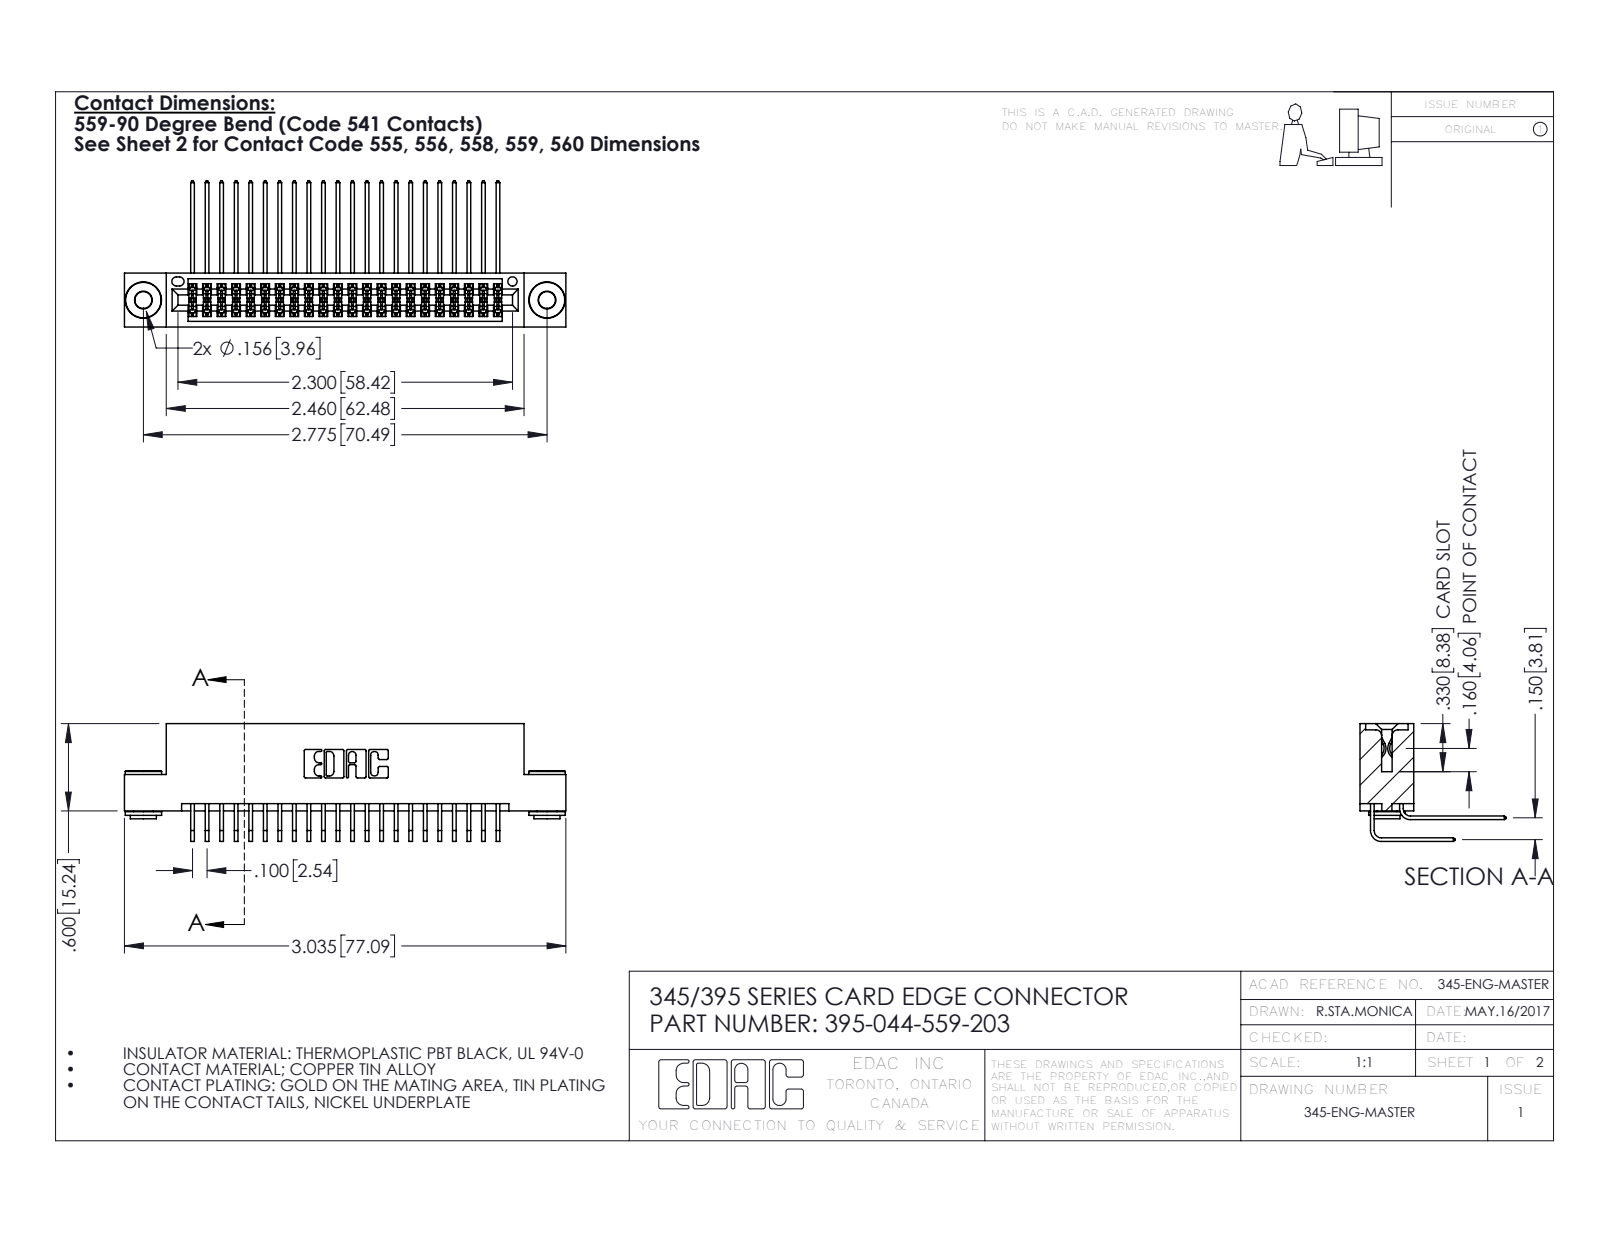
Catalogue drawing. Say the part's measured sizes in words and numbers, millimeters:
The part is named "345-292-001_558 559 Tail - 1; 345-250-002_345-250-002-102; 345 Part_Flush Mounting Lugs - 0.156 Dia-TH; 345-292-001_559 Tail - 2 (+1 more)". Its 3-D file was written by "SolidWorks 2016 (CONFIG_CONTROL_DESIGN)". It is 47 solids with 2452 faces: 1630 planar, 814 cylindrical and 8 other. Overall it measures 77.1 by 25.5 by 20.5 millimeters. Its volume is 7 570 cubic millimeters and its surface area 12 210 square millimeters. Round holes: 2 of diameter 2.9, 2 of diameter 4, 1 of diameter 1.6. Round bosses or shafts: 2 of diameter 6.4, 2 of diameter 4.6, 2 of diameter 3.5. Partial cylindrical surfaces (rounded edges, fillets, slot ends): 67 of radius 0.2, 22 of radius 0.3, 6 of radius 0.2, 6 of radius 0.8, 3 of radius 0.7, 2 of radius 0.4, 2 of radius 0.5, 2 of radius 0.6. The main face-to-face distances are 1.8, 7.6, 5.1, 9.4, 0.6, 2.5, 6.9, 5.7, 3.8, 4.4. The hole center spacings are 6.9, 64.5, 70.5.
